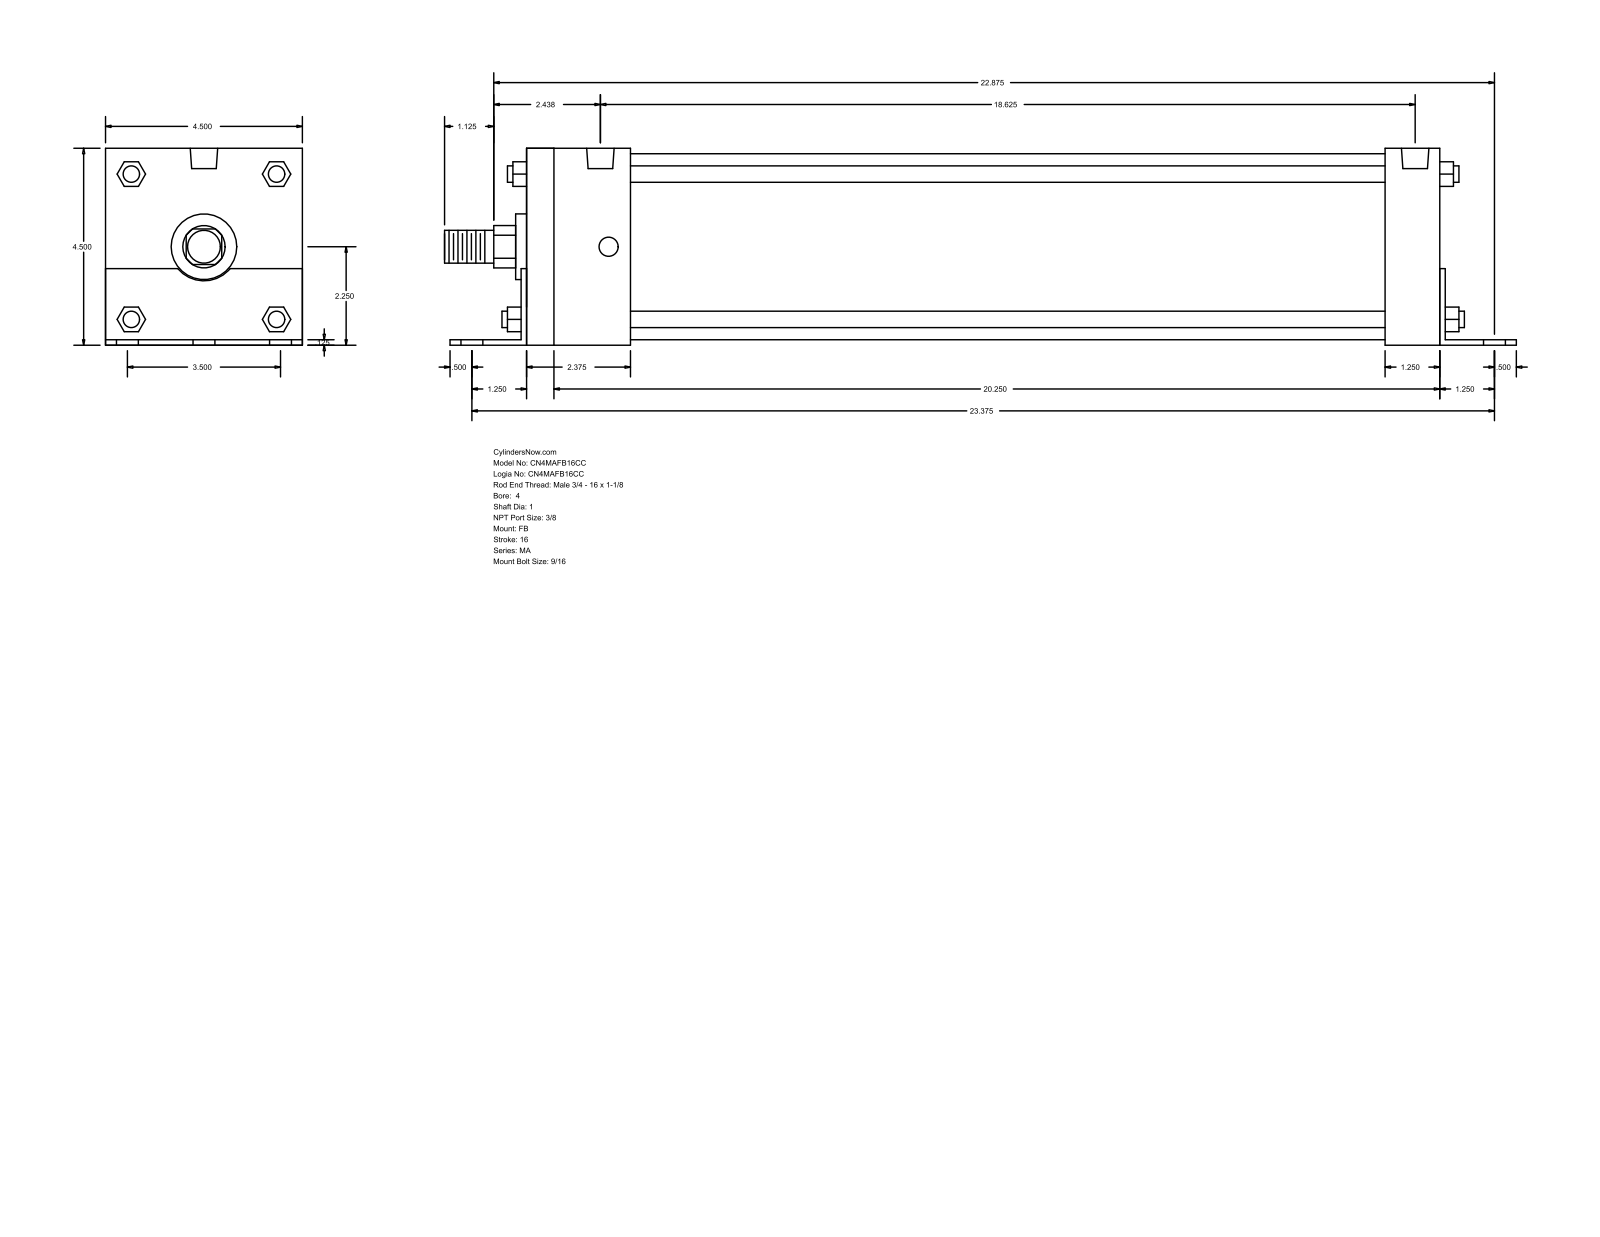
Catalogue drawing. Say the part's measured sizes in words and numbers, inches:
The part is named "MA_FB__0400_1". Its 3-D file was written by "GSSL Pune (CONFIG_CONTROL_DESIGN)". It is 0 solids with 140 faces: 105 planar, 35 cylindrical and 0 other. Overall it measures 24.5 by 4.502 by 4.5 inches. Round holes: 6 of diameter 0.563, 4 of diameter 0.437, 2 of diameter 0.627. Round bosses or shafts: 4 of diameter 0.375, 1 of diameter 4.25, 1 of diameter 1.5, 1 of diameter 1, 1 of diameter 0.75. Partial cylindrical surfaces (rounded edges, fillets, slot ends): 1 of radius 0.484, 1 of radius 0.78. The main face-to-face distances are 4.5, 0.125, 4.502, 0.123, 4.377, 20.875, 0.125, 21.125, 21, 21. The hole center spacings are 1.75, 23.44, 23.375, 0.187, 2.519, 2.657, 3.419, 3.5.
